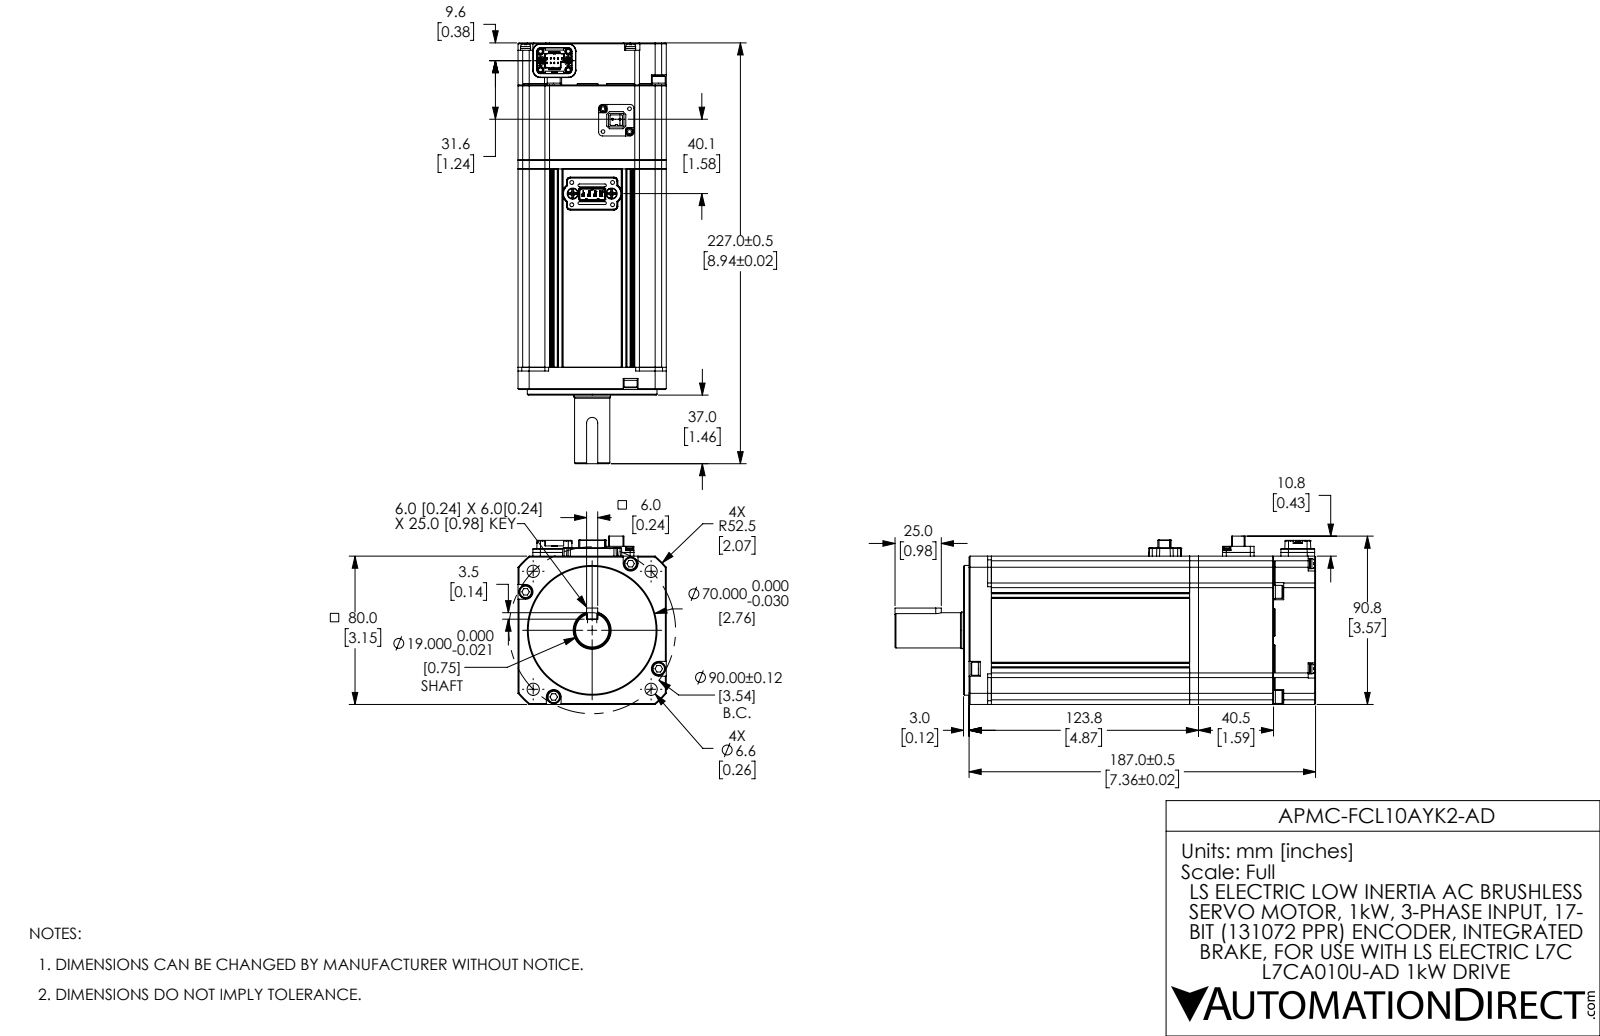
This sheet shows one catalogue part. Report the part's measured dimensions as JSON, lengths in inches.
{"part_name": "APMC-FCL10AYK2-AD", "step_written_by": "SolidWorks 2017 (AUTOMOTIVE_DESIGN)", "units": "inches", "bodies": {"solids": 50, "faces": 2072, "planar": 1317, "cylindrical": 552, "other": 203}, "overall_size": [8.937, 3.575, 3.15], "volume_in3": 65.51, "surface_area_in2": 236.7, "round_holes": [[0.083, 10], [0.157, 8], [0.177, 8], [0.079, 6], [0.118, 6], [0.138, 4], [0.26, 4], [0.039, 2], [0.236, 2], [0.13, 1], [0.134, 1], [0.512, 1]], "round_bosses_or_shafts": [[0.283, 8], [0.276, 8], [0.213, 6], [0.165, 2], [0.142, 2], [0.138, 2], [0.087, 2], [0.035, 2]], "partial_cylinders_radius": [[0.012, 36], [0.008, 20], [0.079, 12], [0.039, 10], [0.006, 9], [0.098, 9], [0.157, 9], [0.018, 7]], "face_to_face_distances": [3.15, 0.189, 1.811, 4.402, 4.213, 1.594, 1.783, 5.996, 0.028, 1.622], "hole_center_spacings": [1.634, 0.465, 2.076, 2.311, 2.703, 3.376, 0.197, 0.237]}
